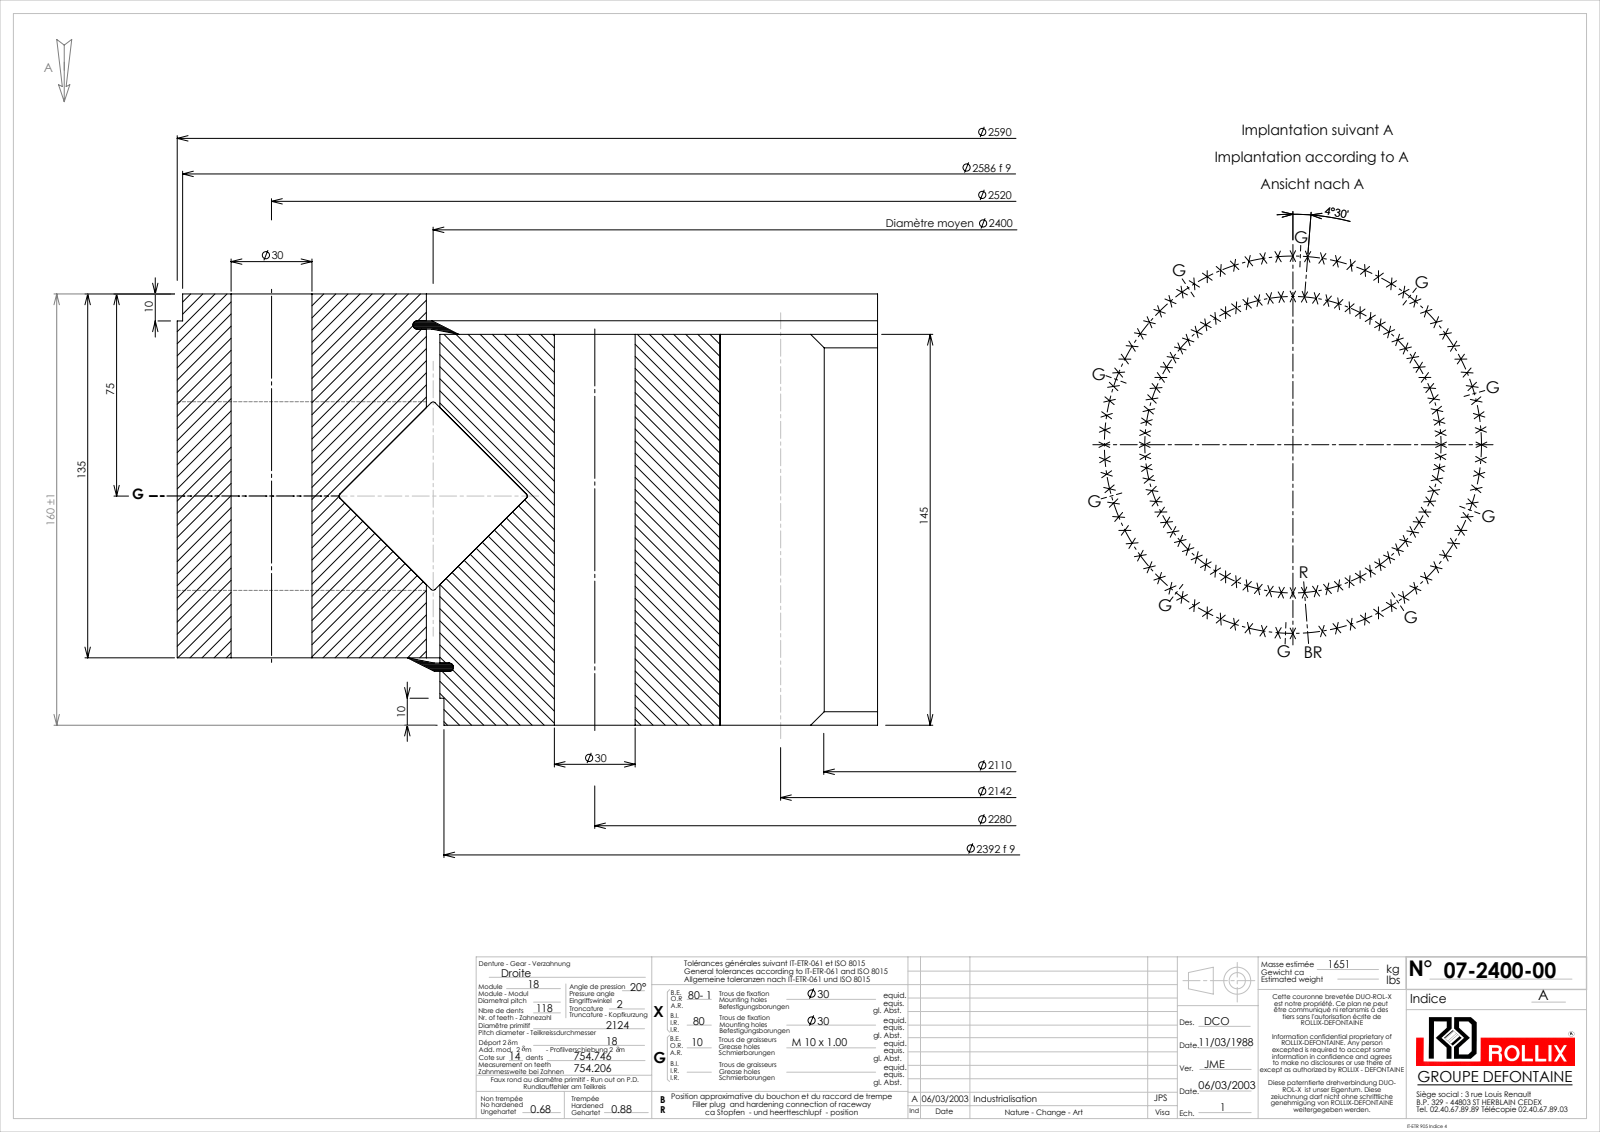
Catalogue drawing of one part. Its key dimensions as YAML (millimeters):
part_name: "07-2400-00"
step_written_by: "SolidWorks 2016 (CONFIG_CONTROL_DESIGN)"
units: millimeters
bodies: {solids: 5, faces: 1130, planar: 252, cylindrical: 595, other: 283}
overall_size: [2590, 2590, 160]
volume: 195000000
surface_area: 11310000
round_holes:
  - {diameter: 30, count: 159}
  - {diameter: 9, count: 10}
  - {diameter: 2405, count: 1}
round_bosses_or_shafts:
  - {diameter: 2590, count: 1}
  - {diameter: 2586, count: 1}
  - {diameter: 2395, count: 1}
  - {diameter: 2392, count: 1}
  - {diameter: 50, count: 1}
partial_cylinders:
  - {radius: 1055, count: 1}
  - {radius: 1093.5, count: 1}
face_to_face_distances: [145, 25, 120, 15, 135, 160, 5.05, 125.05, 3.1, 1.95]
hole_center_spacings: [89.51, 356.67, 532.25, 178.89, 267.98, 618.88, 704.56, 789.15]
